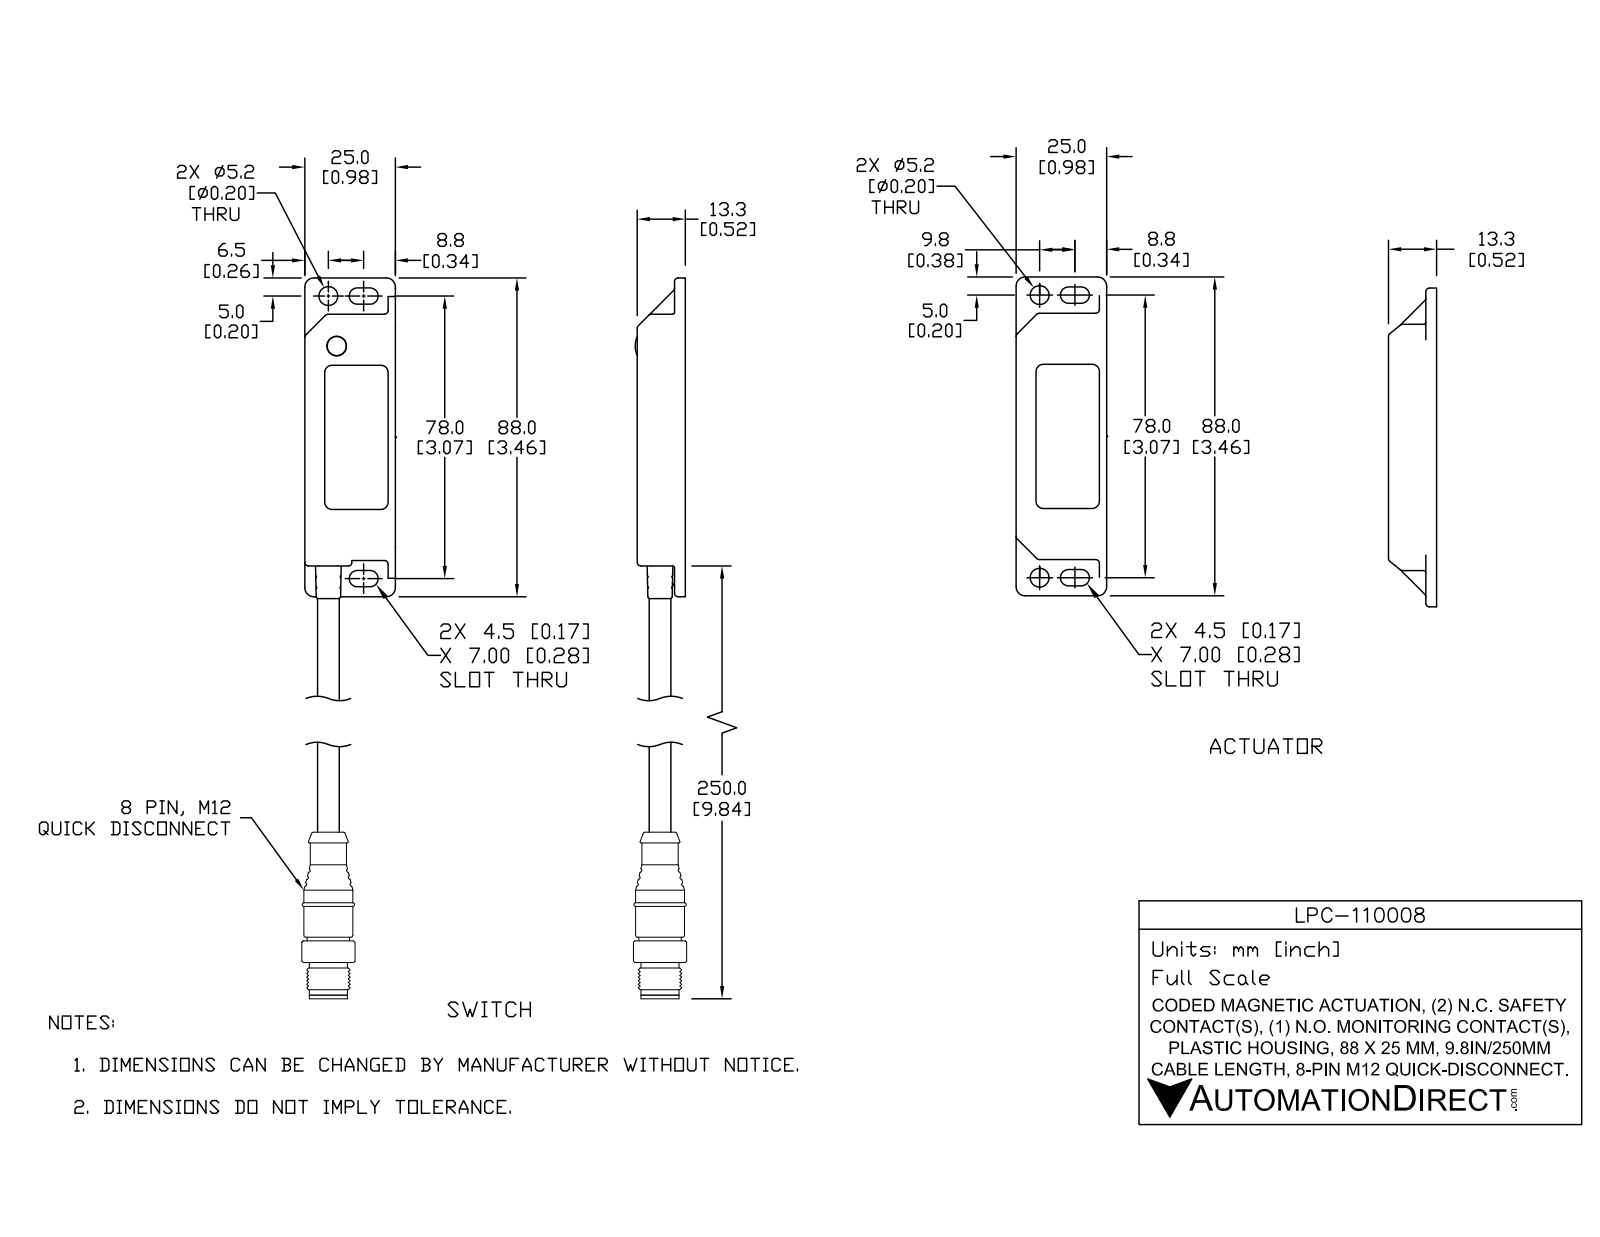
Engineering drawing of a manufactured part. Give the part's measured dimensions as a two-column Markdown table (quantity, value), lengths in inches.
| quantity | value |
| --- | --- |
| part name | LPC-110008 |
| STEP written by | SolidWorks 2017 (AUTOMOTIVE_DESIGN) |
| units | inches |
| bodies | 8 solids, 987 faces (379 planar, 297 cylindrical, 311 other) |
| overall size | 12.972 × 1.03 × 0.579 |
| volume | 1.411 in³ |
| surface area | 35.11 in² |
| round holes (diameter × count) | 0.197 × 2, 0.205 × 2, 0.119 × 1, 0.173 × 1, 0.213 × 1, 0.232 × 1, 0.276 × 1, 0.327 × 1, 0.465 × 1 |
| round bosses / shafts (diameter × count) | 0.031 × 8, 0.091 × 2, 0.079 × 2, 0.531 × 1, 0.461 × 1, 0.413 × 1, 0.394 × 1, 0.374 × 1 |
| partial cylindrical surfaces (radius × count) | 0.02 × 63, 0.039 × 29, 0.012 × 6, 0.079 × 4, 0.089 × 4, 0.098 × 4, 0.189 × 1, 0.289 × 1 |
| main face-to-face distances | 0.067, 0.441, 0.079, 0.374, 0.059, 0.071, 0.508, 0.445, 0.984, 0.512 |
| hole center spacings | 0.748, 2.457, 0.306, 0.551, 1.783, 1.906, 2.529, 3.071 |
